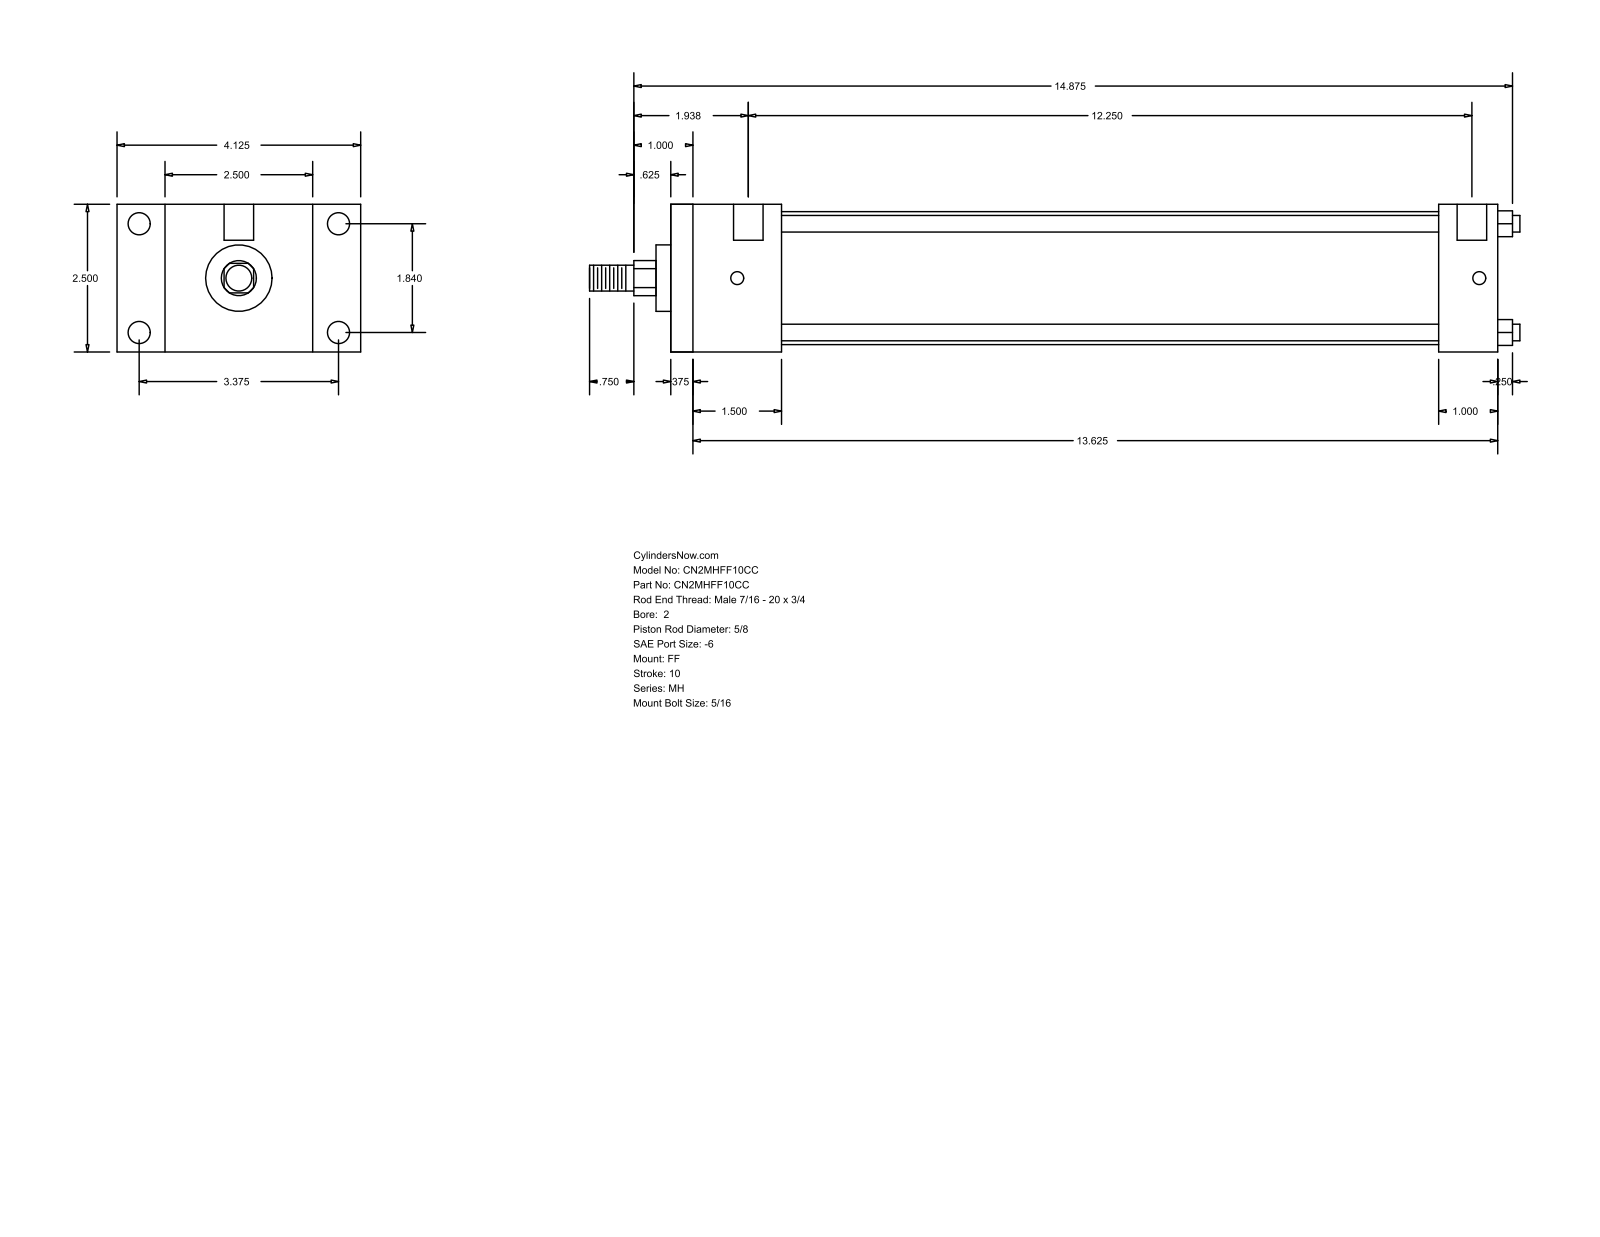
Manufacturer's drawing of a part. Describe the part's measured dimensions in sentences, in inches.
The part is named "MH_FF__0200_0.625". Its 3-D file was written by "GSSL Pune (CONFIG_CONTROL_DESIGN)". It is 0 solids with 92 faces: 64 planar, 28 cylindrical and 0 other. Overall it measures 15.75 by 4.125 by 2.5 inches. Round holes: 4 of diameter 0.219, 4 of diameter 0.375, 2 of diameter 0.5. Round bosses or shafts: 4 of diameter 0.281, 1 of diameter 2.25, 1 of diameter 1.125, 1 of diameter 0.625, 1 of diameter 0.437. Partial cylindrical surfaces (rounded edges, fillets, slot ends): 1 of radius 0.297. The main face-to-face distances are 2.5, 14, 0.375, 13.625, 1.5, 1.875, 13, 12.625, 11.125, 12.125. The hole center spacings are 1.84, 3.375, 3.844, 12.563, 0.125, 0.187, 12.25, 12.375.
